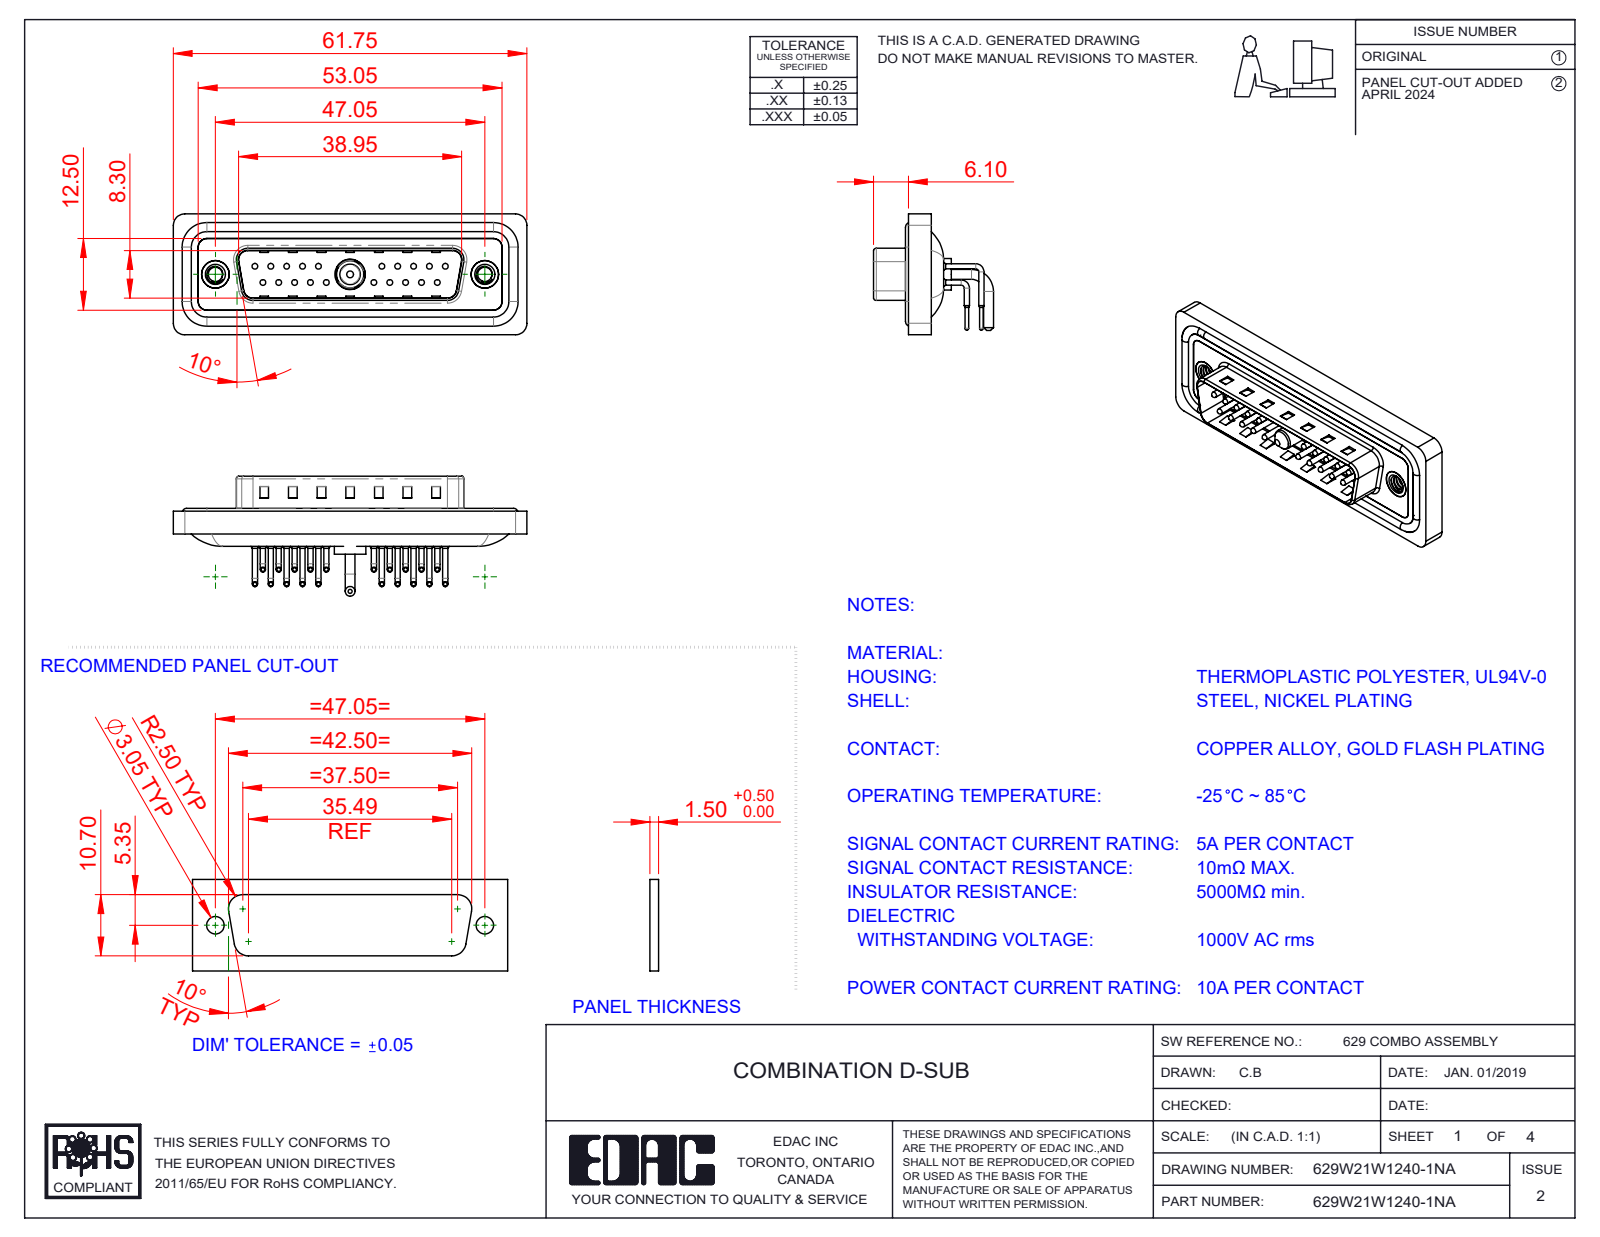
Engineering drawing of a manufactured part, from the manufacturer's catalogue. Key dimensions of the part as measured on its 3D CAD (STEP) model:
Part name (STEP PRODUCT): 629Combo Contact Row 2; 629Combo Threaded Rivet_A; Power Pin_10A RA; 629Combo Contact Row 1 (+5 more)
STEP written by: SolidWorks 2023 (CONFIG_CONTROL_DESIGN)
Units: millimetres
Bodies: 29 solids, 2720 faces (1499 planar, 927 cylindrical, 294 other)
Overall size (bounding box): 61.75 × 21.1 × 20.95
Volume: 7 364 mm³ · Surface area: 12 674 mm²
Round holes (diameter × count): ⌀0.75 ×20, ⌀1.6 ×20, ⌀2 ×20, ⌀2.5 ×2, ⌀4 ×2, ⌀4.8 ×2, ⌀5 ×2, ⌀4.85 ×1, ⌀5.3 ×1
Round bosses / shafts (diameter × count): ⌀0.9 ×40, ⌀1.5 ×20, ⌀1 ×20, ⌀0.65 ×20, ⌀1.6 ×4, ⌀4.9 ×2, ⌀1.7 ×2, ⌀5.5 ×1
Partial cylindrical surfaces — rounded edges, fillets, slot ends (radius × count): R1.01 ×20, R1.5 ×18, R2 ×18, R0.5 ×8, R1.6 ×8, R0.25 ×4, R0.6 ×4, R0.65 ×4
Main face-to-face distances: 0.4, 2.9, 0.8, 4.1, 1.1, 2.1, 1.6, 4.5, 1.5, 2.5
Hole centre spacings: 3.16, 2.77, 5.54, 8.31, 5.04, 19.39, 20.97, 22.16
